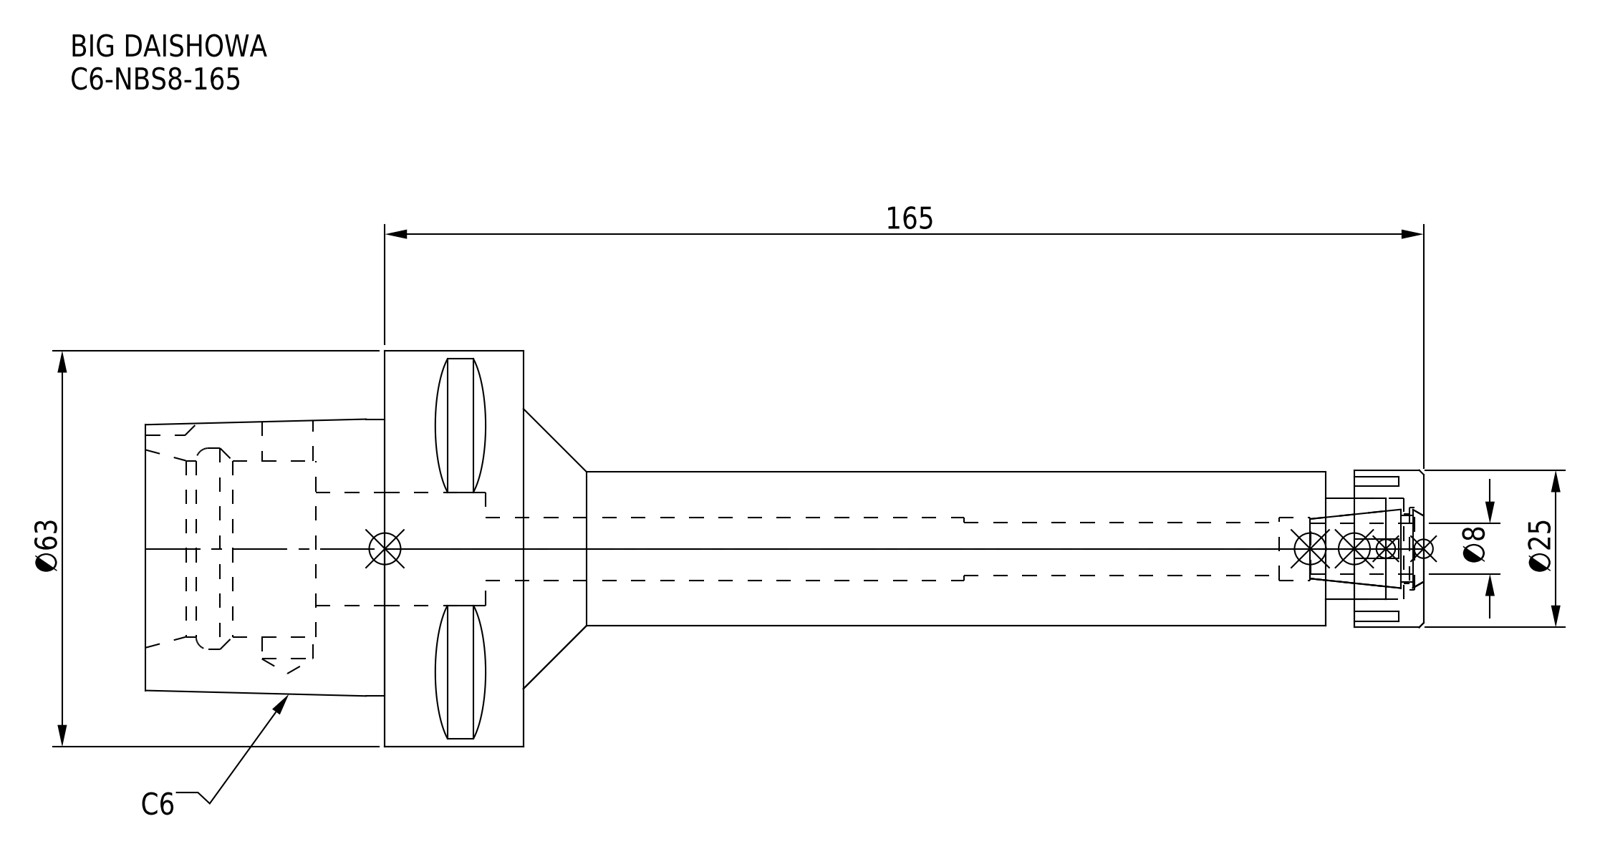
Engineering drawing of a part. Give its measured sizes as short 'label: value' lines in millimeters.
name: NBN8_1.stp; DXF_TEMP_ASSY_ASM_4_ASM.stp; C6-NBS8-165_1.stp; C6-NBS8-165.stp (+3 more)
written by: SolidWorks 2019 (CONFIG_CONTROL_DESIGN)
unit: mm
bodies: 2 solids, 112 faces (61 planar, 33 cylindrical, 18 other)
size: 203 × 63 × 63
volume: 156 559 mm³; area: 36 567 mm²
holes: 1× ⌀8.1, 1× ⌀8.4, 1× ⌀10, 1× ⌀11, 1× ⌀13, 1× ⌀16, 1× ⌀18, 1× ⌀28, 1× ⌀32
bosses: 1× ⌀63, 1× ⌀25, 1× ⌀24.5
rounds: 1× R5
face distances: 22, 11, 165, 27, 60, 38, 143, 33, 176, 203
